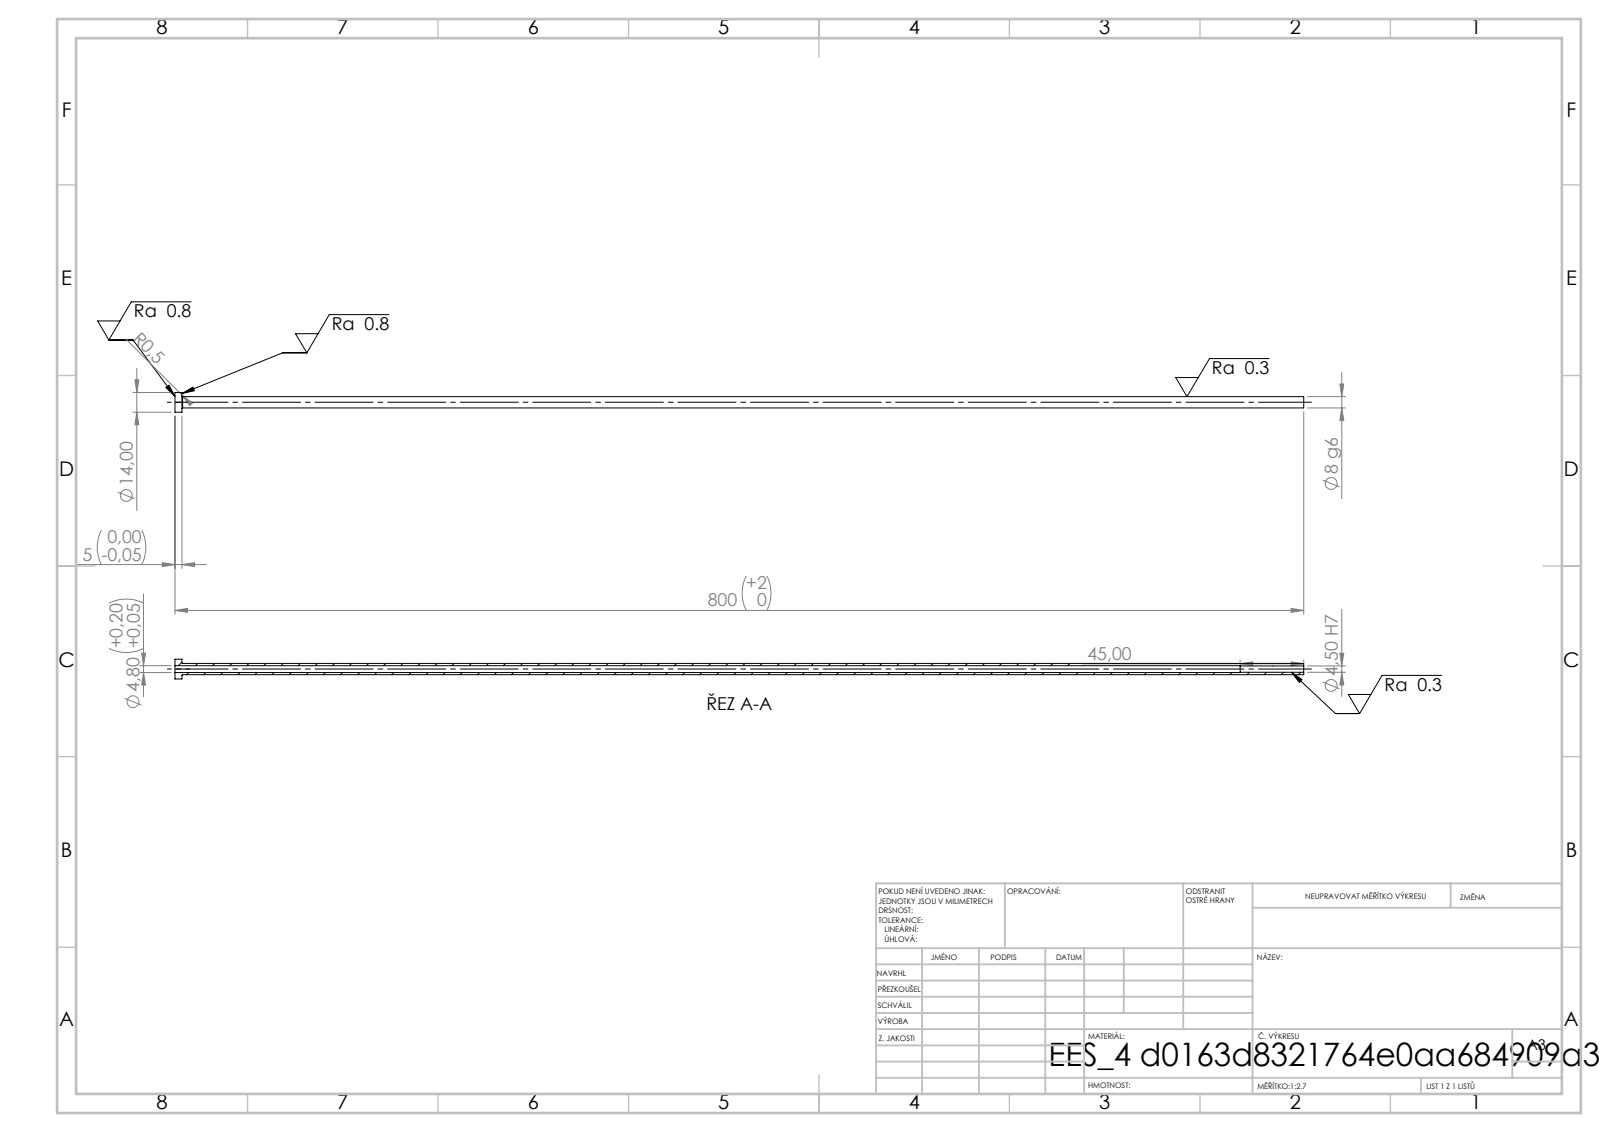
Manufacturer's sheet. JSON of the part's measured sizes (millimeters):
{"step_written_by": "SolidWorks 2019 (CONFIG_CONTROL_DESIGN)", "units": "millimeters", "bodies": {"solids": 1, "faces": 14, "planar": 4, "cylindrical": 8, "other": 2}, "overall_size": [800, 14, 14], "volume_mm3": 26354, "surface_area_mm2": 32493, "round_holes": [[4.5, 1], [4.8, 1]], "round_bosses_or_shafts": [[14, 1], [8, 1]], "face_to_face_distances": [5, 800, 795, 755, 750, 45]}
